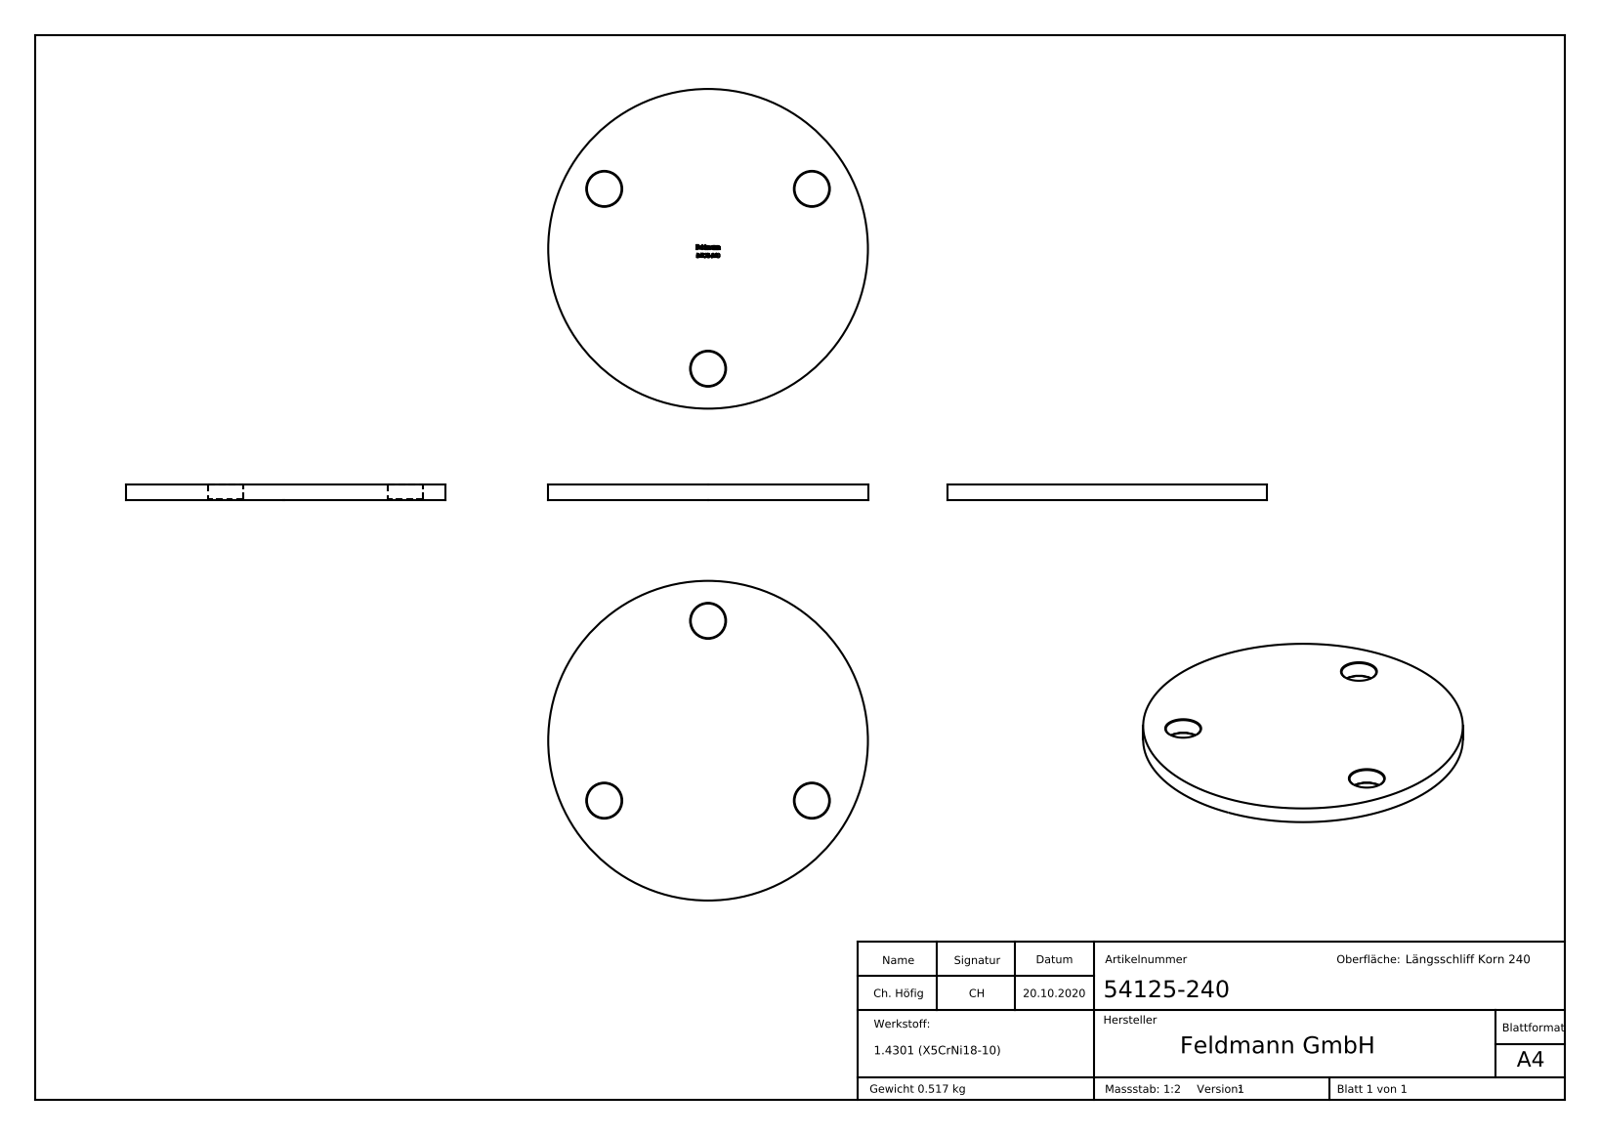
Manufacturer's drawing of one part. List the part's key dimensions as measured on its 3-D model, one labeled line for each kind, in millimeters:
Part name (STEP PRODUCT): 54125-240
STEP written by: SolidWorks 2018 (CONFIG_CONTROL_DESIGN)
Units: millimetres
Bodies: 1 solid, 244 faces (139 planar, 8 cylindrical, 97 other)
Overall size (bounding box): 120 × 120 × 6
Volume: 65 461 mm³ · Surface area: 24 794 mm²
Round holes (diameter × count): ⌀13 ×3
Round bosses / shafts (diameter × count): ⌀120 ×1
Main face-to-face distances: 6, 5.9, 0.39, 2.97, 1.26, 1.19, 4.23, 3.19, 3.39, 0.75
Hole centre spacings: 77.94
